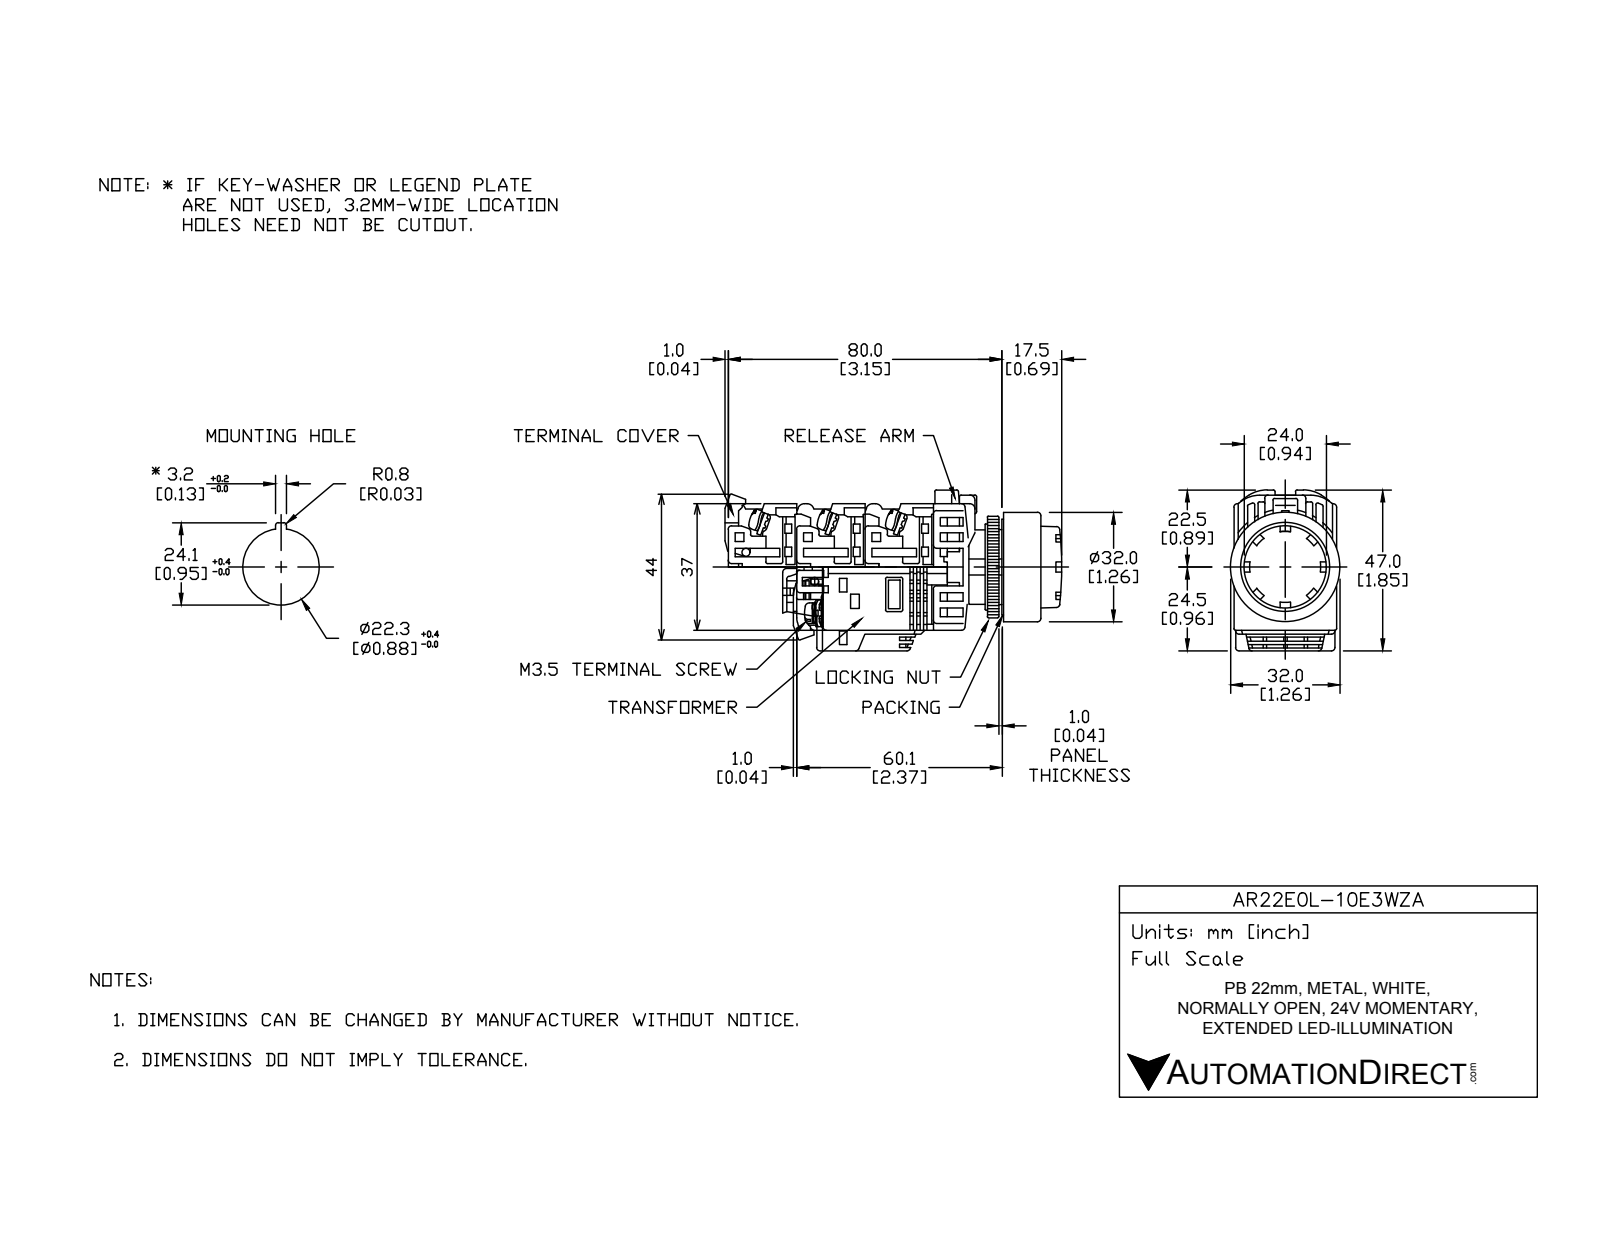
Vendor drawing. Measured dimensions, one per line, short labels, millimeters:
name: AR22E0L-10E3WZA
written by: SolidWorks 2017 (AUTOMOTIVE_DESIGN)
unit: mm
bodies: 18 solids, 475 faces (329 planar, 111 cylindrical, 35 other)
size: 59.25 × 43.81 × 32
volume: 39 258 mm³; area: 24 550 mm²
holes: 1× ⌀21.8, 1× ⌀22, 1× ⌀25, 1× ⌀31
bosses: 4× ⌀5, 1× ⌀32, 1× ⌀30.5, 1× ⌀29.8, 1× ⌀24, 1× ⌀23.8, 1× ⌀21.75, 1× ⌀17
rounds: 39× R0.5, 8× R1.75, 4× R5, 2× R4, 1× R16.59, 1× R17.59
face distances: 1, 18, 28.5, 48.5, 20, 29, 3, 2, 21, 0.5
